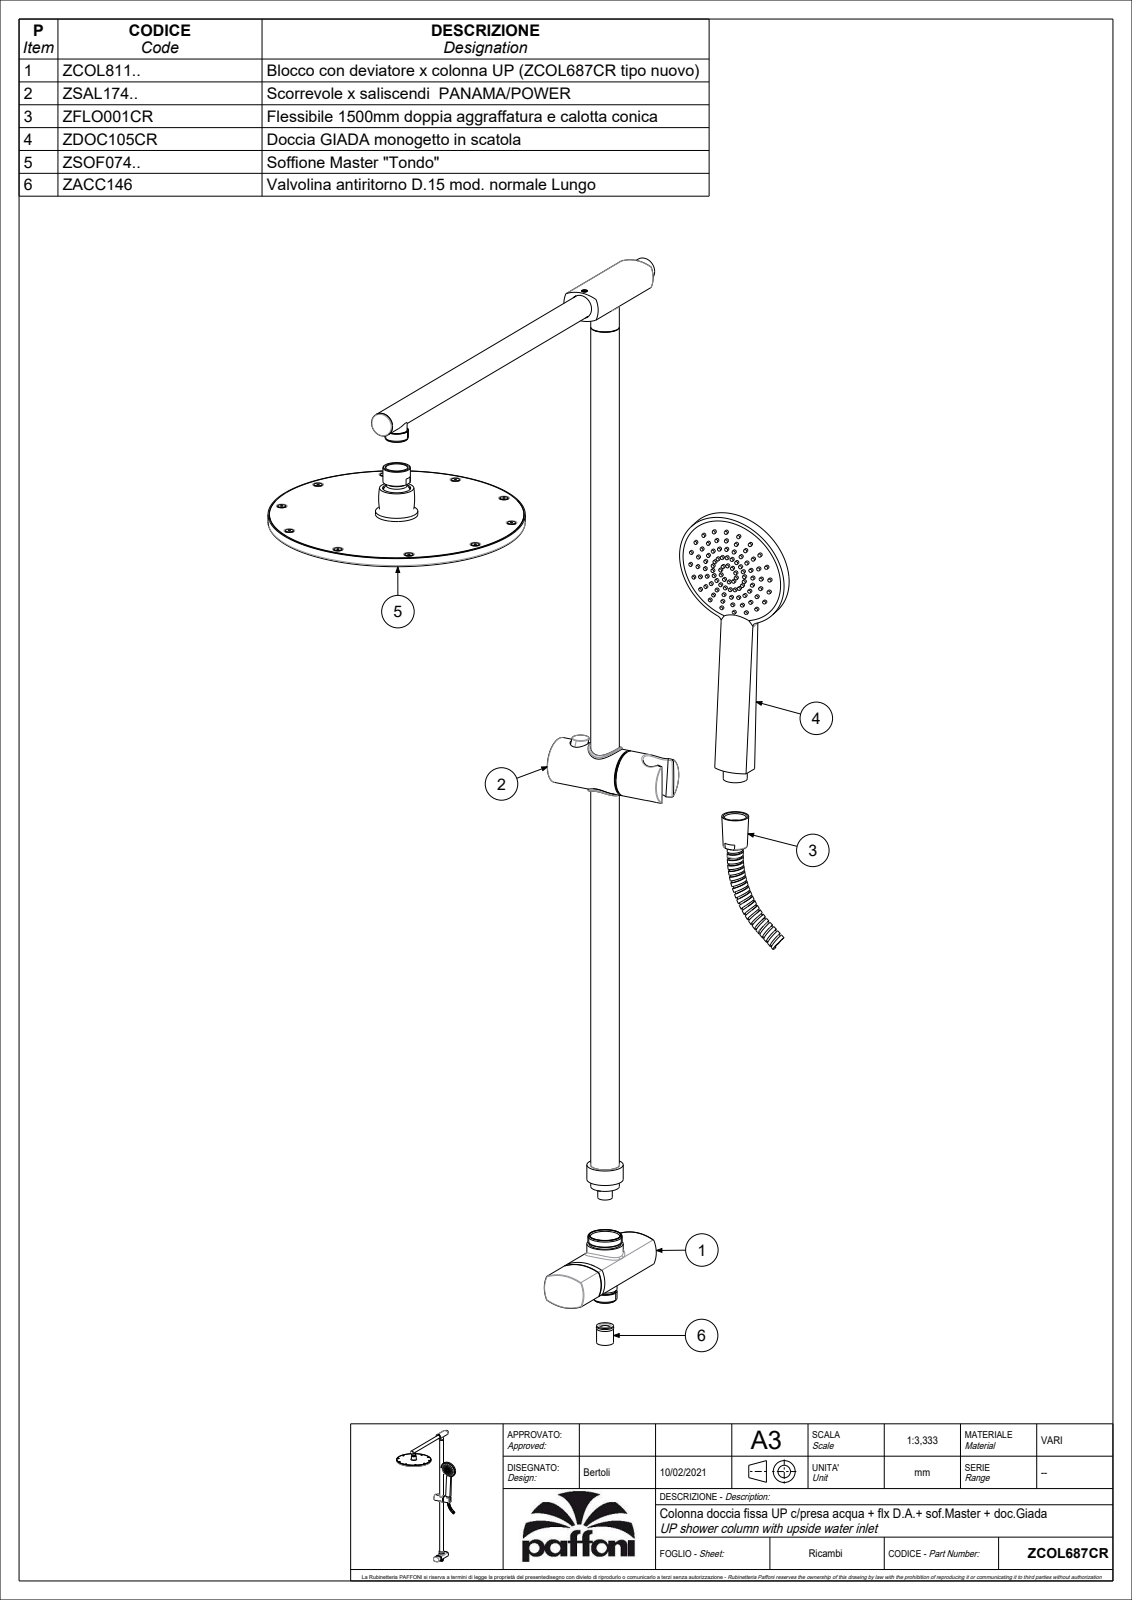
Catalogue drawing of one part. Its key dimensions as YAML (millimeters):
part_name: "ZCOL687CR"
step_written_by: "CREO PARAMETRIC BY PTC INC, 2020044 (CONFIG_CONTROL_DESIGN)"
units: millimeters
bodies: {solids: 1, faces: 5487, planar: 1350, cylindrical: 1810, other: 2327}
overall_size: [890.63, 532, 225]
volume: 716545
surface_area: 594424
round_holes:
  - {diameter: 2, count: 102}
  - {diameter: 4.5, count: 102}
  - {diameter: 8, count: 10}
  - {diameter: 5.5, count: 3}
  - {diameter: 15, count: 3}
  - {diameter: 7.5, count: 2}
  - {diameter: 9, count: 2}
  - {diameter: 10, count: 2}
  - {diameter: 13, count: 2}
  - {diameter: 20, count: 2}
  - {diameter: 4, count: 1}
  - {diameter: 4.2, count: 1}
round_bosses_or_shafts:
  - {diameter: 4, count: 190}
  - {diameter: 3, count: 90}
  - {diameter: 7, count: 11}
  - {diameter: 6, count: 11}
  - {diameter: 5, count: 4}
  - {diameter: 18, count: 3}
  - {diameter: 25, count: 2}
  - {diameter: 24, count: 2}
partial_cylinders:
  - {radius: 0.3, count: 68}
  - {radius: 1, count: 57}
  - {radius: 0.5, count: 45}
  - {radius: 2, count: 34}
  - {radius: 0.2, count: 28}
  - {radius: 1.5, count: 17}
  - {radius: 3, count: 12}
  - {radius: 5.5, count: 11}
face_to_face_distances: [1, 8.3, 7.3, 5.7, 2.6, 4.7, 0.5, 4.2, 6.8, 1.5]
hole_center_spacings: [23.75, 52.8, 58.54, 13, 20.07, 32.28, 43.76, 30.58]
